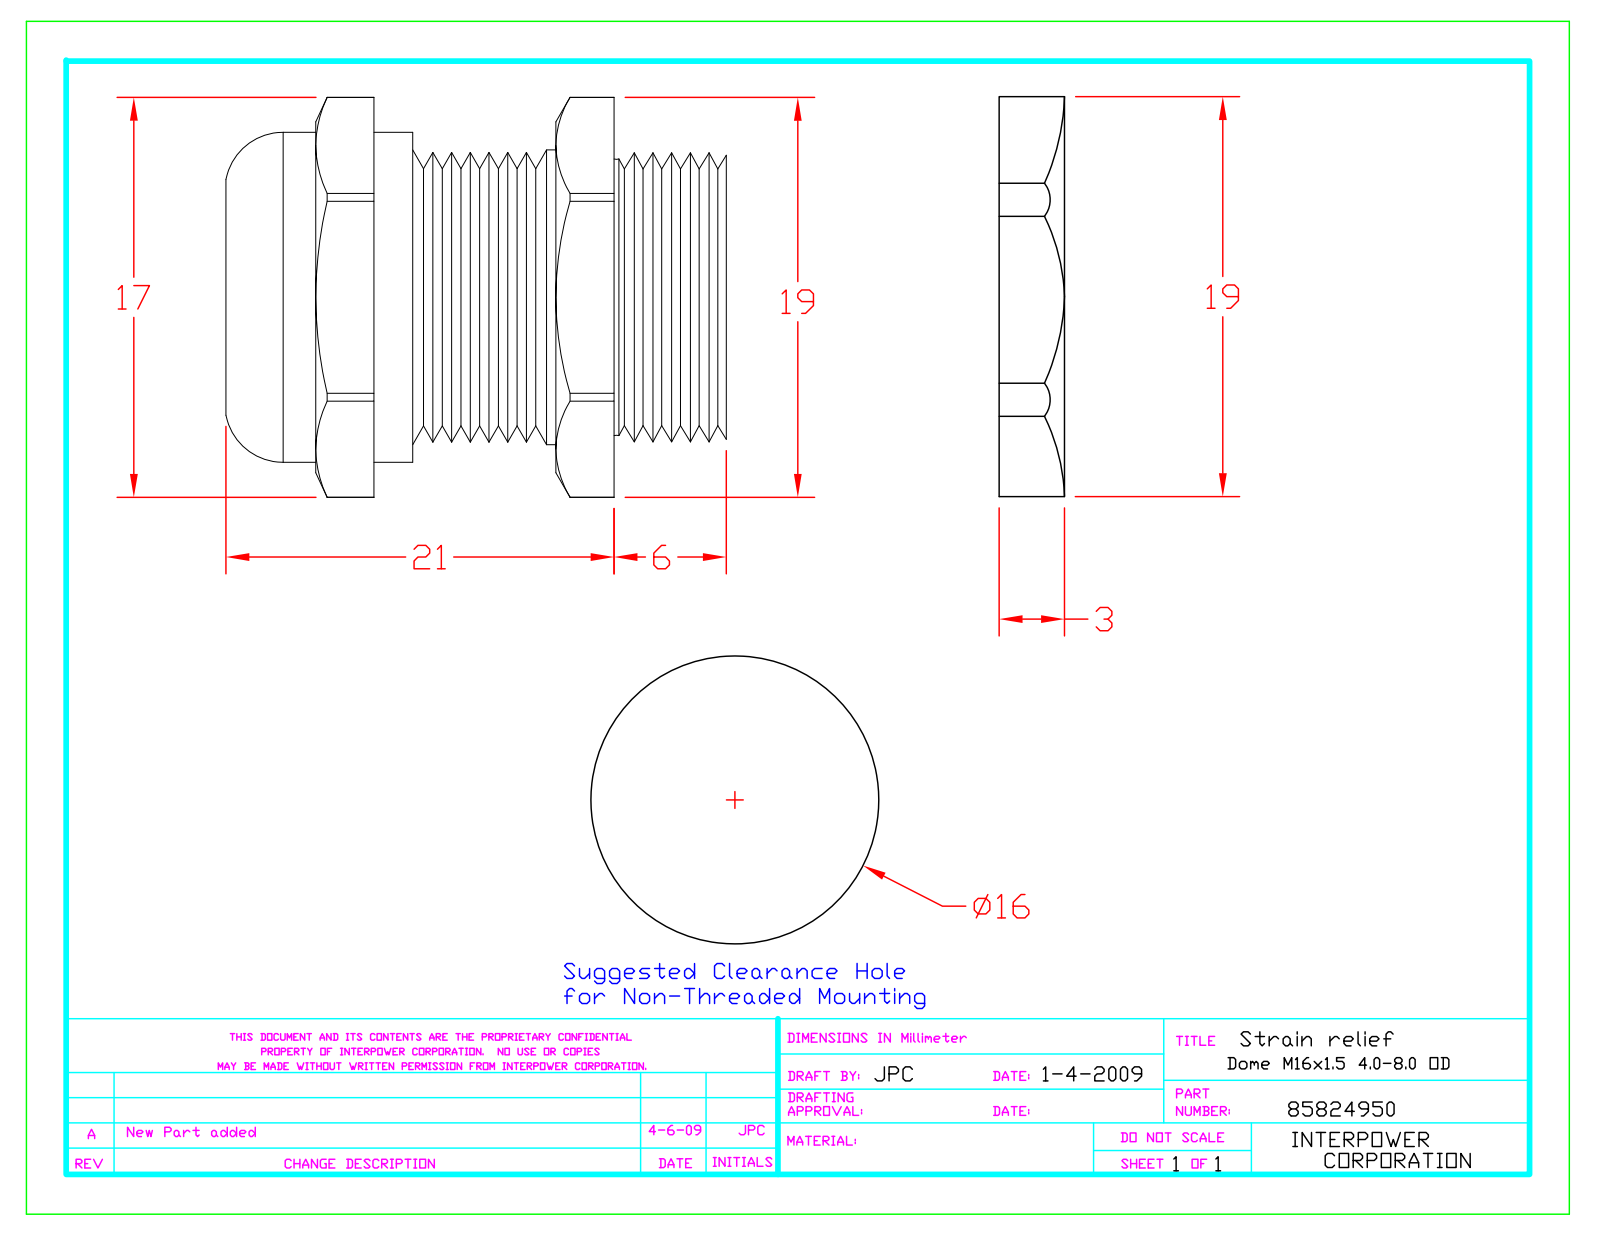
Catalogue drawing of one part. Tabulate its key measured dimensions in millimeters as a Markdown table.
| quantity | value |
| --- | --- |
| part name | CD16MA-BR |
| STEP written by | SolidWorks 2007 (CONFIG_CONTROL_DESIGN) |
| units | millimeters |
| bodies | 2 solids, 121 faces (21 planar, 26 cylindrical, 74 other) |
| overall size | 27.2 × 21.7 × 19.1 |
| volume | 3 880 mm³ |
| surface area | 4 019 mm² |
| round holes (diameter × count) | 9.4 × 1, 12.8 × 1 |
| round bosses / shafts (diameter × count) | 17.9 × 1, 16 × 1 |
| partial cylindrical surfaces (radius × count) | 10.8 × 1 |
| main face-to-face distances | 3.1, 13, 19.1, 22.3, 16.2, 6.1, 9.3, 9.9, 19.2, 19.1 |
